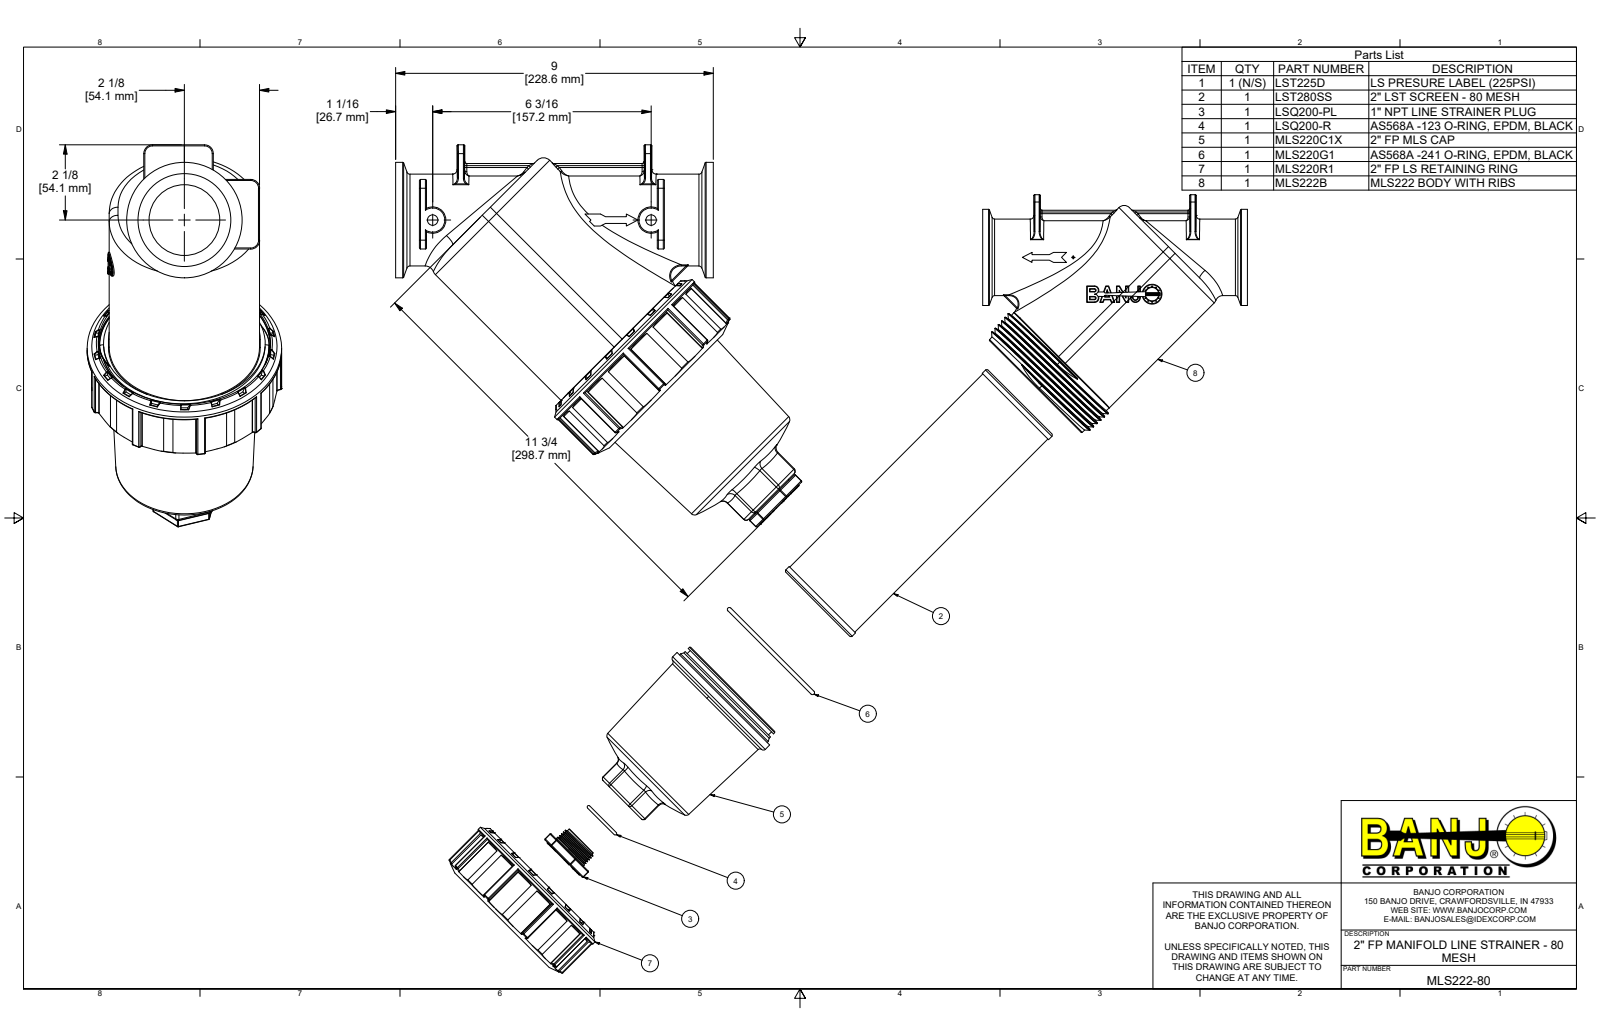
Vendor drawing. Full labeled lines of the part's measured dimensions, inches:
Part name (STEP PRODUCT): MLS222-80; MLS222B; MLS220C1; MLS220C1X (+5 more)
STEP written by: Autodesk Inventor 2022 (AUTOMOTIVE_DESIGN)
Units: inches
Bodies: 7 solids, 1902 faces (759 planar, 338 cylindrical, 805 other)
Overall size (bounding box): 11.507 × 10.817 × 5.51
Volume: 90.38 in³ · Surface area: 737.5 in²
Round holes (diameter × count): ⌀0.295 ×2, ⌀0.454 ×1, ⌀0.641 ×1, ⌀0.75 ×1, ⌀1 ×1, ⌀2 ×1, ⌀2.63 ×1, ⌀2.937 ×1, ⌀3.53 ×1, ⌀4.13 ×1, ⌀4.175 ×1, ⌀4.5 ×1
Round bosses / shafts (diameter × count): ⌀3.188 ×2, ⌀5.51 ×1, ⌀5.25 ×1, ⌀4.45 ×1, ⌀4.215 ×1, ⌀4.1 ×1, ⌀3.905 ×1, ⌀3.27 ×1
Partial cylindrical surfaces — rounded edges, fillets, slot ends (radius × count): R0.03 ×76, R0.01 ×36, R0.06 ×12, R0.09 ×12, R0.25 ×8, R0.125 ×6, R0.02 ×2, R0.039 ×2
Main face-to-face distances: 0.1, 8.9, 0.3, 9, 5.809, 6.109, 5.3, 0.2, 6.74, 1.096
Hole centre spacings: 2.522, 4.191, 6.19
